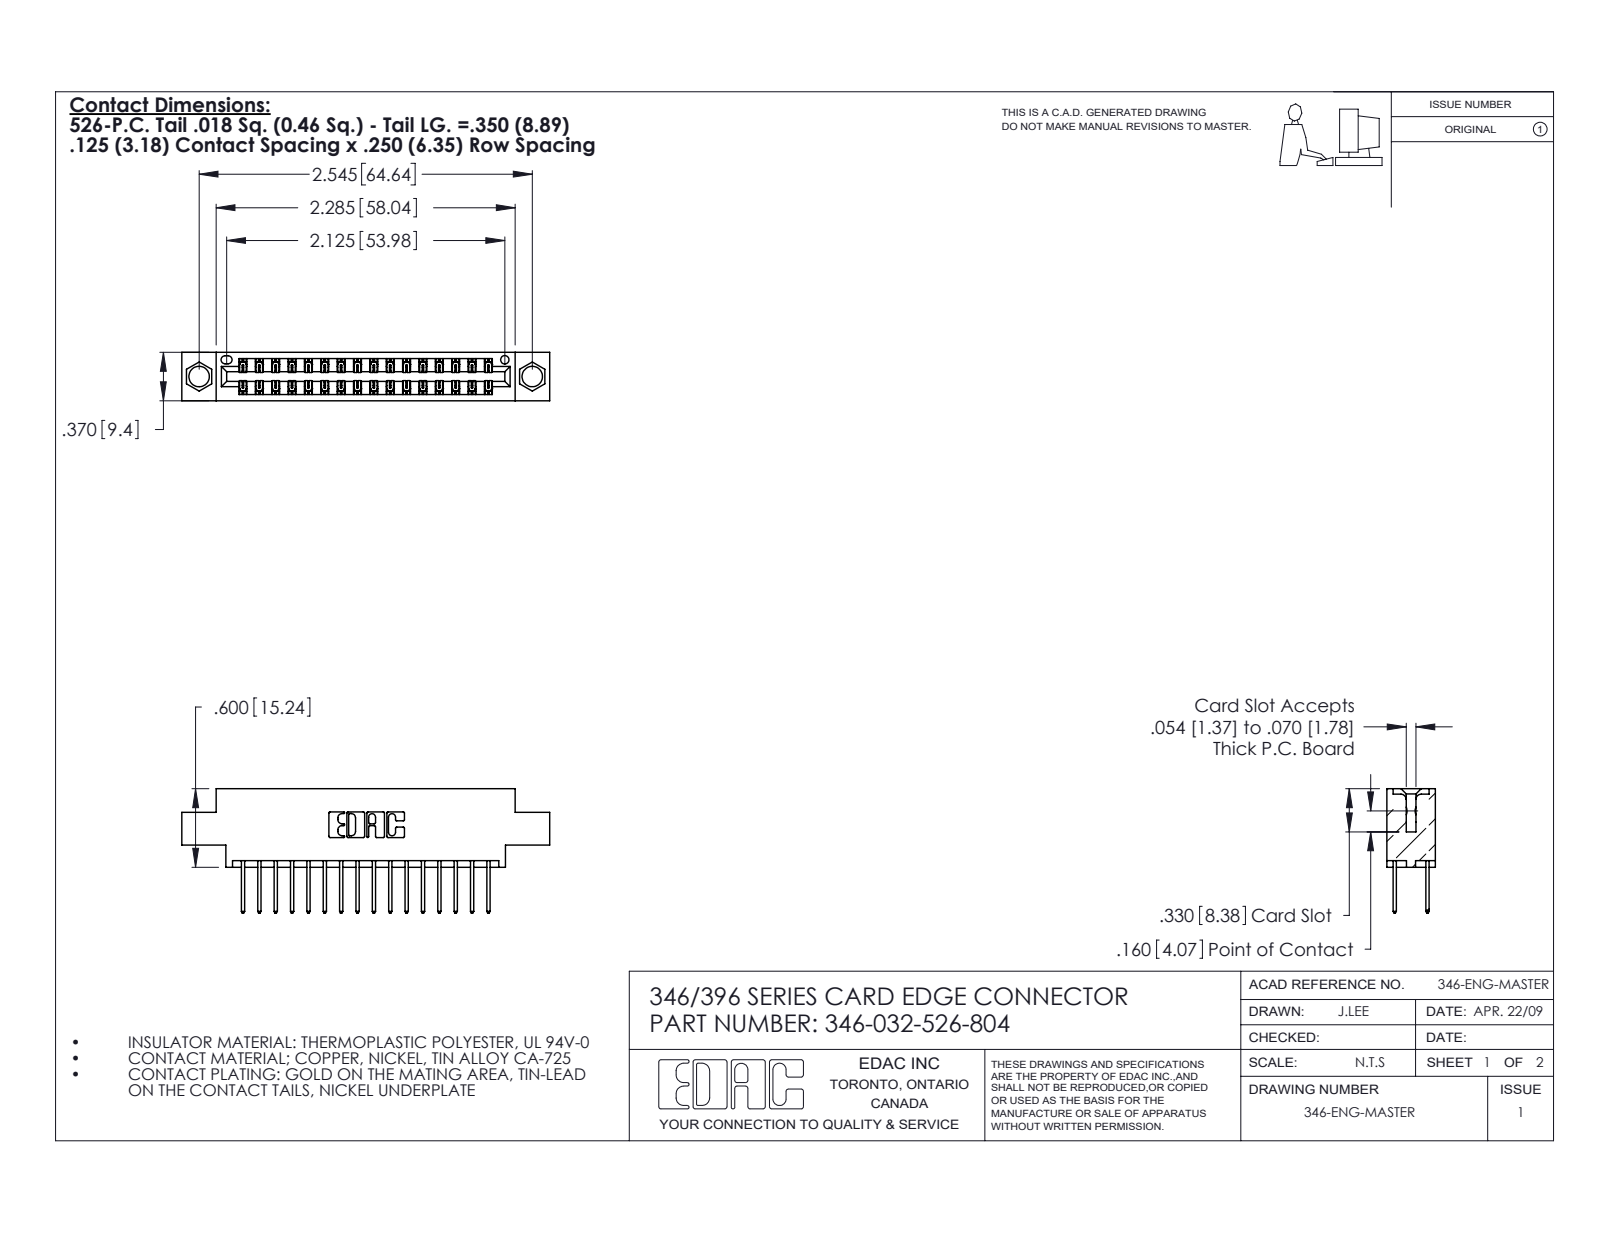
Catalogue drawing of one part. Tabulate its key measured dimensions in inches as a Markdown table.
| quantity | value |
| --- | --- |
| part name | 346 Part_0.170 Offset - 0.156 Dia-TH; 345-292-001_345-293-126; 346-032-526-804 |
| STEP written by | SolidWorks 2020 (CONFIG_CONTROL_DESIGN) |
| units | inches |
| bodies | 33 solids, 1804 faces (1214 planar, 590 cylindrical, 0 other) |
| overall size | 2.81 × 0.95 × 0.37 |
| volume | 0.4 in³ |
| surface area | 13.73 in² |
| round holes (diameter × count) | 0.156 × 2, 0.064 × 1 |
| partial cylindrical surfaces (radius × count) | 0.006 × 48, 0.01 × 32, 0.01 × 22, 0.007 × 6, 0.031 × 6, 0.026 × 3, 0.014 × 2, 0.022 × 2 |
| main face-to-face distances | 0.048, 0.322, 0.25, 0.37, 0.072, 0.298, 0.025, 0.275, 0.222, 0.148 |
| hole center spacings | 0.246, 2.338, 2.545 |
